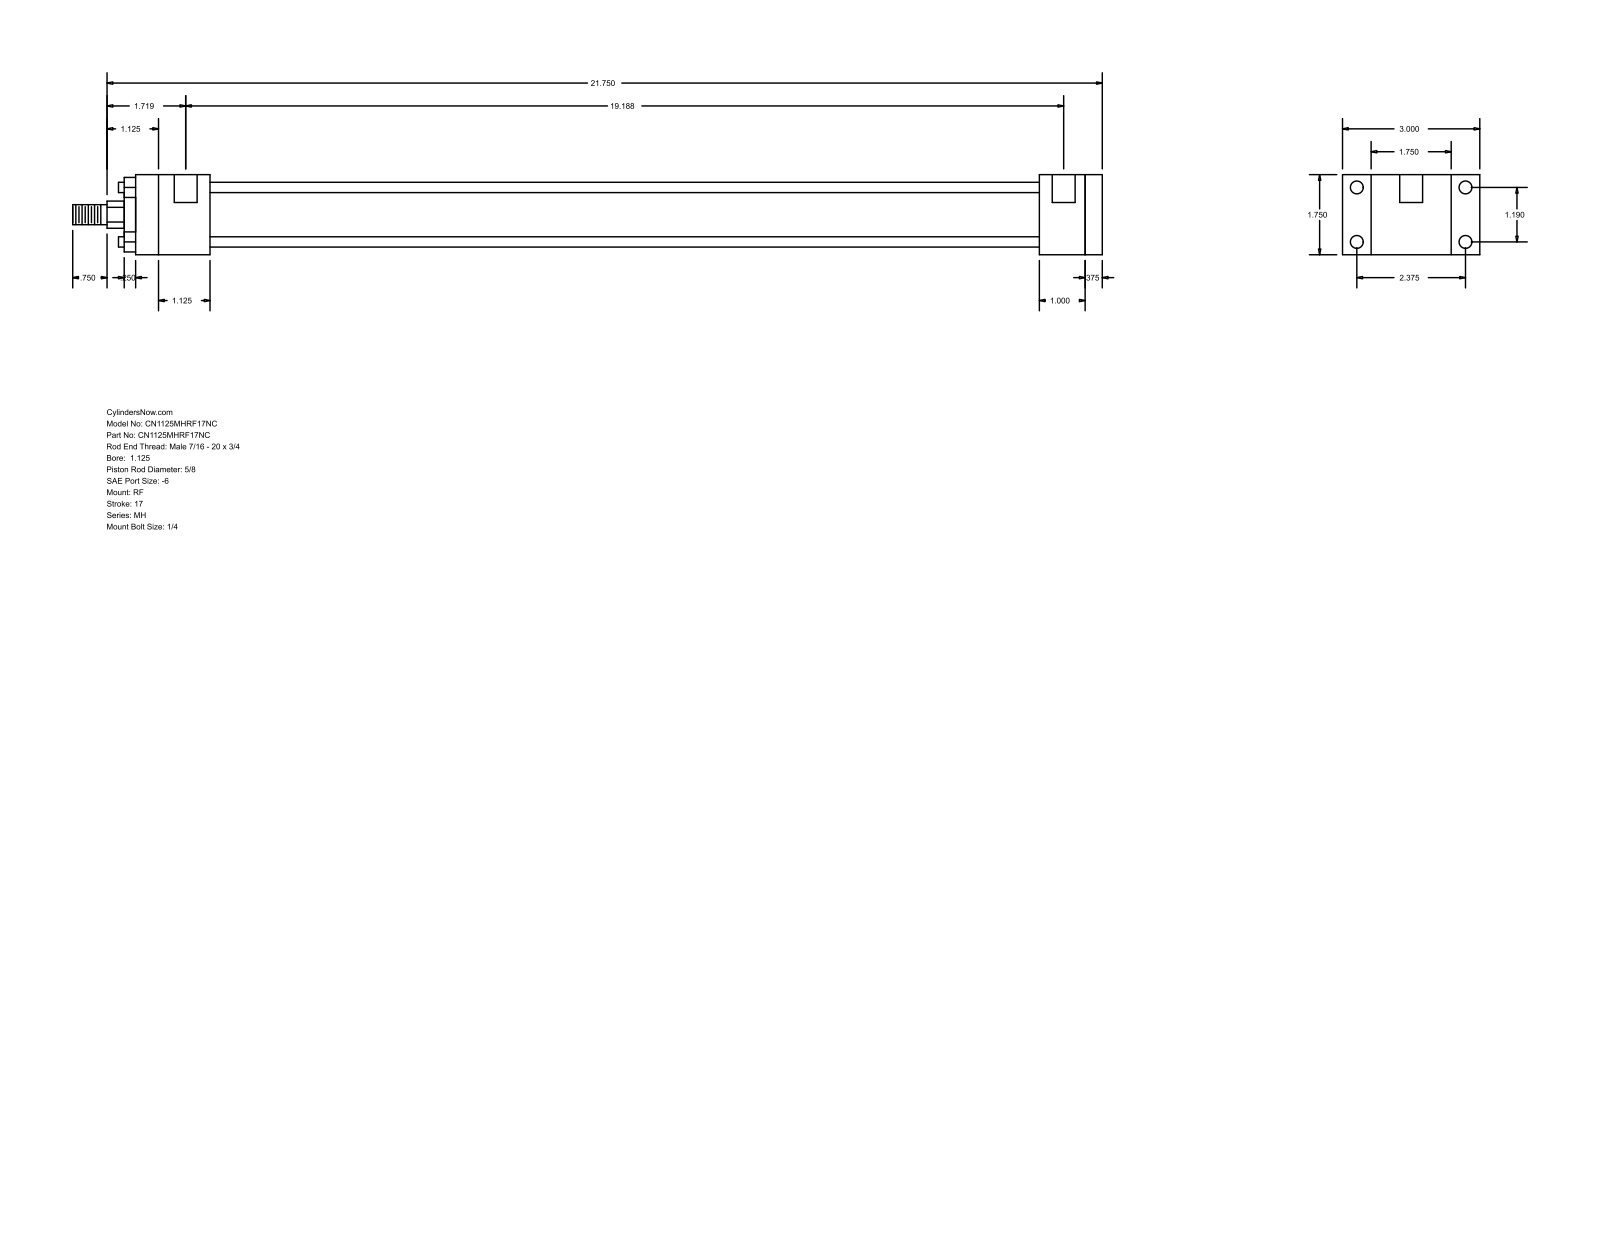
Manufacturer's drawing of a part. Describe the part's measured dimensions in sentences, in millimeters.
The part is named "MH_RF__0112_0.625". Its 3-D file was written by "GSSL Pune (CONFIG_CONTROL_DESIGN)". It is 0 solids with 92 faces: 64 planar, 28 cylindrical and 0 other. Overall it measures 571.5 by 76.2 by 44.45 millimeters. Round holes: 4 of diameter 5.56, 4 of diameter 7.14, 2 of diameter 12.7. Round bosses or shafts: 4 of diameter 5.71, 1 of diameter 34.92, 1 of diameter 28.57, 1 of diameter 15.88, 1 of diameter 11.11. Partial cylindrical surfaces (rounded edges, fillets, slot ends): 1 of radius 7.54. The main face-to-face distances are 44.46, 9.53, 536.57, 25.4, 34.93, 15.87, 485.77, 495.3, 460.37, 41.27. The hole center spacings are 30.22, 60.32, 67.47, 484.19, 3.17, 487.36.
